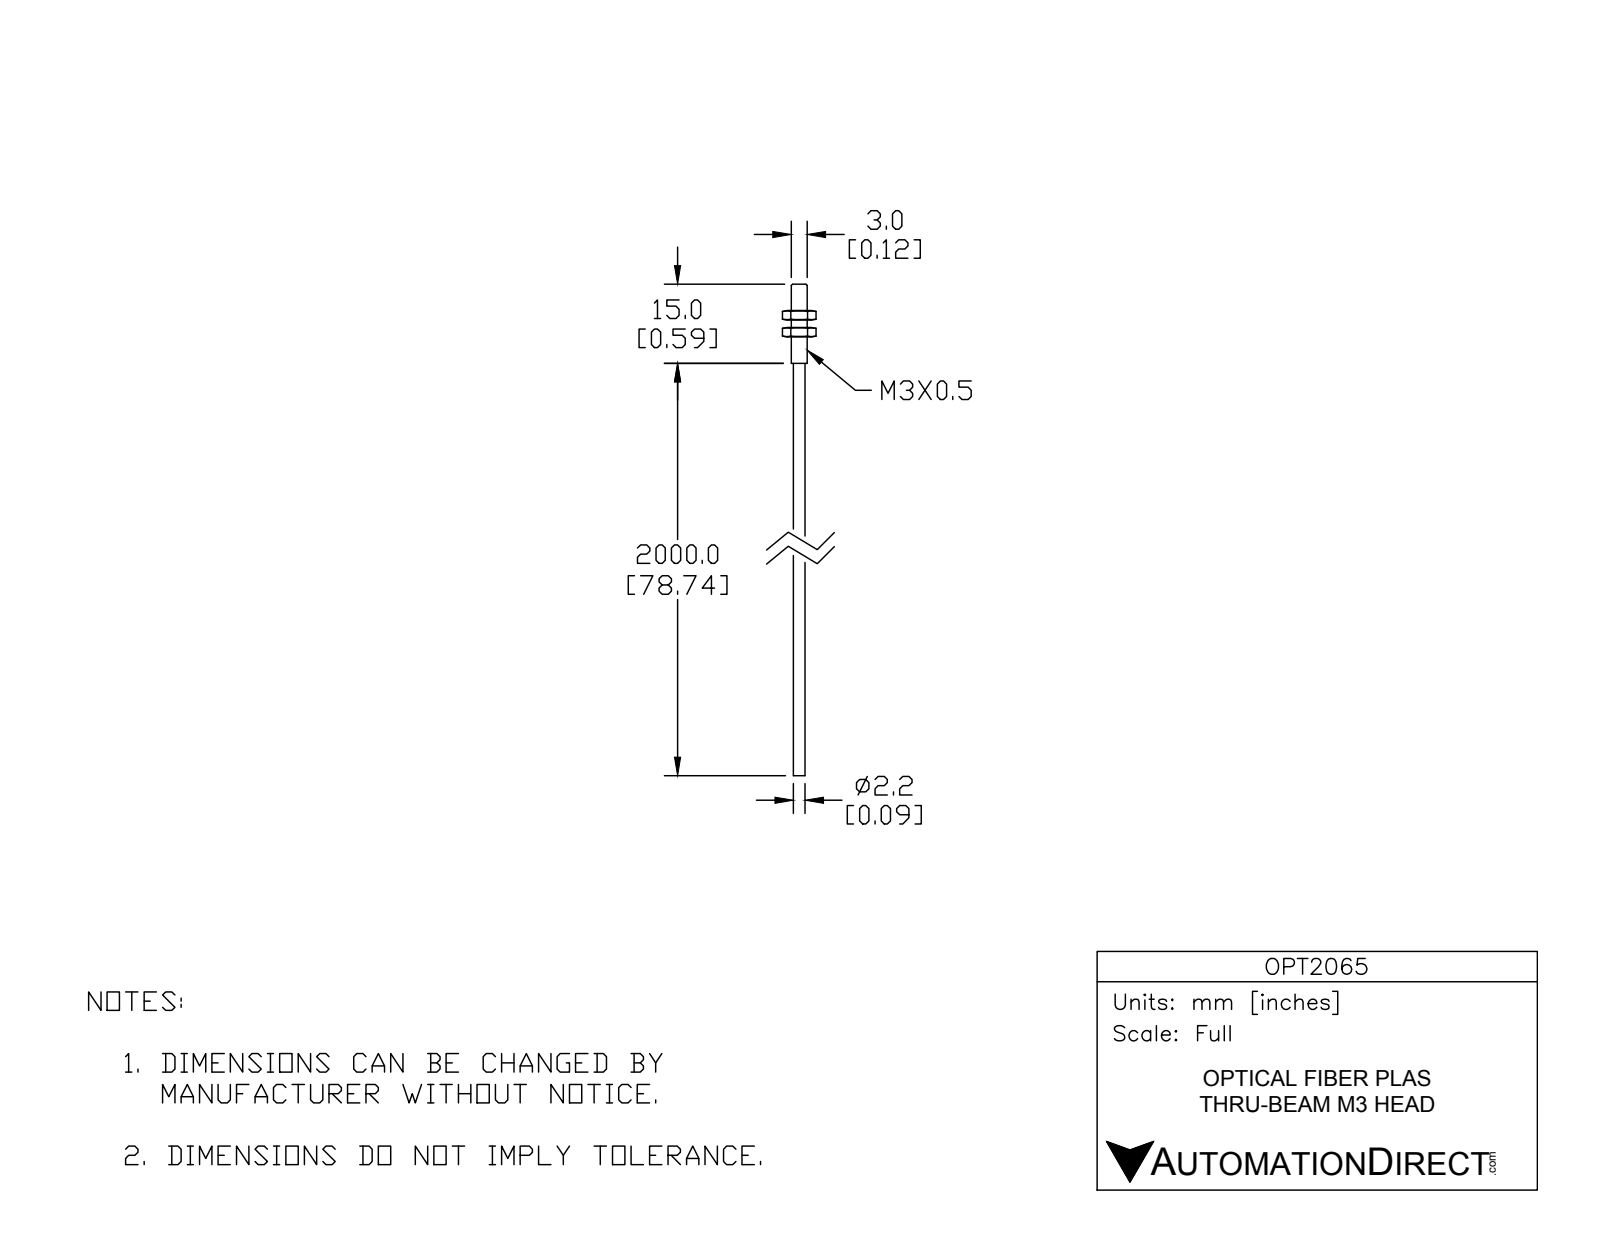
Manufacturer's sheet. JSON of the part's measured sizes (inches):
{"part_name": "OPT2065", "step_written_by": "SolidWorks 2014 (AUTOMOTIVE_DESIGN)", "units": "inches", "bodies": {"solids": 2, "faces": 41, "planar": 21, "cylindrical": 10, "other": 10}, "overall_size": [3.661, 0.25, 0.217], "volume_in3": 0.027, "surface_area_in2": 1.172, "round_bosses_or_shafts": [[0.118, 1], [0.087, 1]], "face_to_face_distances": [0.217, 0.071, 0.126, 0.197, 0.055, 0.268, 0.323, 0.394, 0.259, 3.661]}
